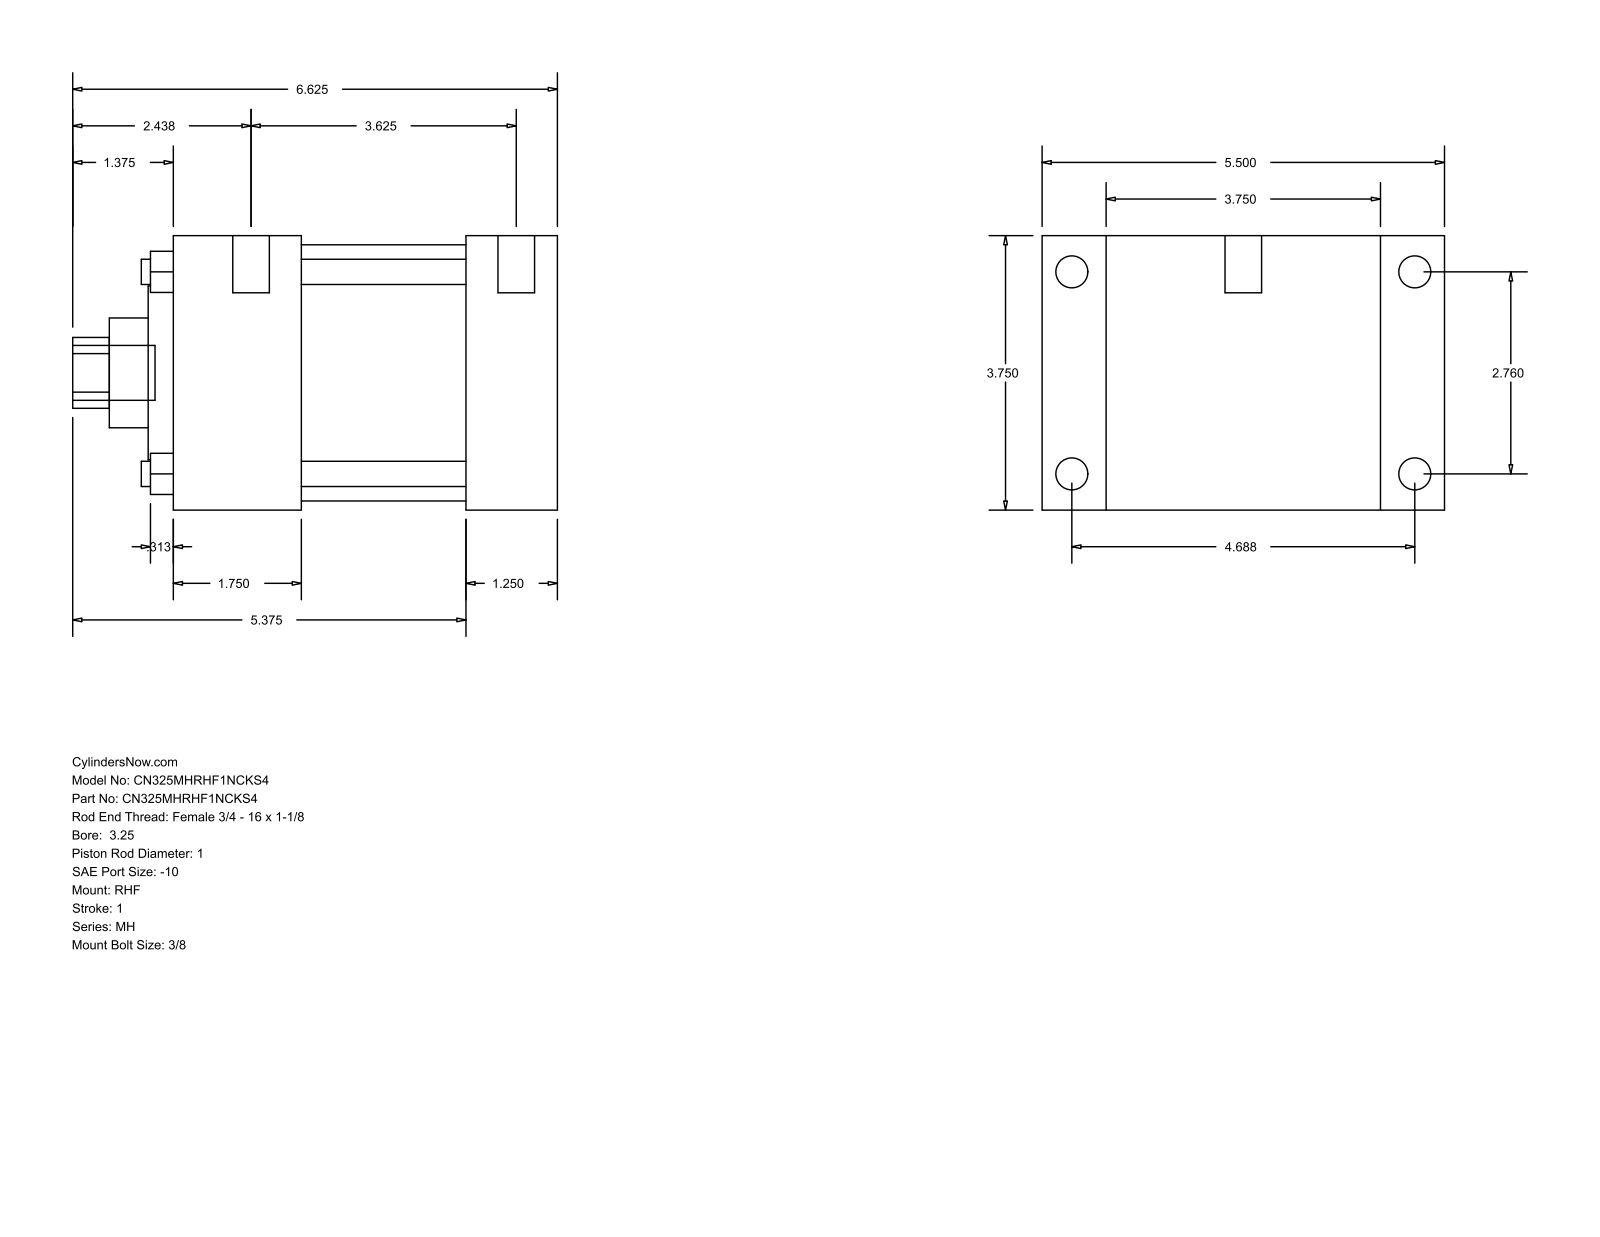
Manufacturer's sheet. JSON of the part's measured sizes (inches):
{"part_name": "MH_RHF__0325_1", "step_written_by": "GSSL Pune (CONFIG_CONTROL_DESIGN)", "units": "inches", "bodies": {"solids": 0, "faces": 90, "planar": 61, "cylindrical": 29, "other": 0}, "overall_size": [6.625, 5.5, 3.75], "round_holes": [[0.345, 4], [1, 1], [1.5, 1], [2.375, 1], [3.5, 1]], "round_bosses_or_shafts": [[0.438, 4], [0.219, 4], [0.5, 2], [0.75, 1]], "partial_cylinders_radius": [[0.484, 1]], "face_to_face_distances": [3.75, 1.25, 0.875, 4.625, 4, 5.25, 5.5, 1.75, 2.25, 3.5], "hole_center_spacings": [1.952, 2.76, 3.903]}
